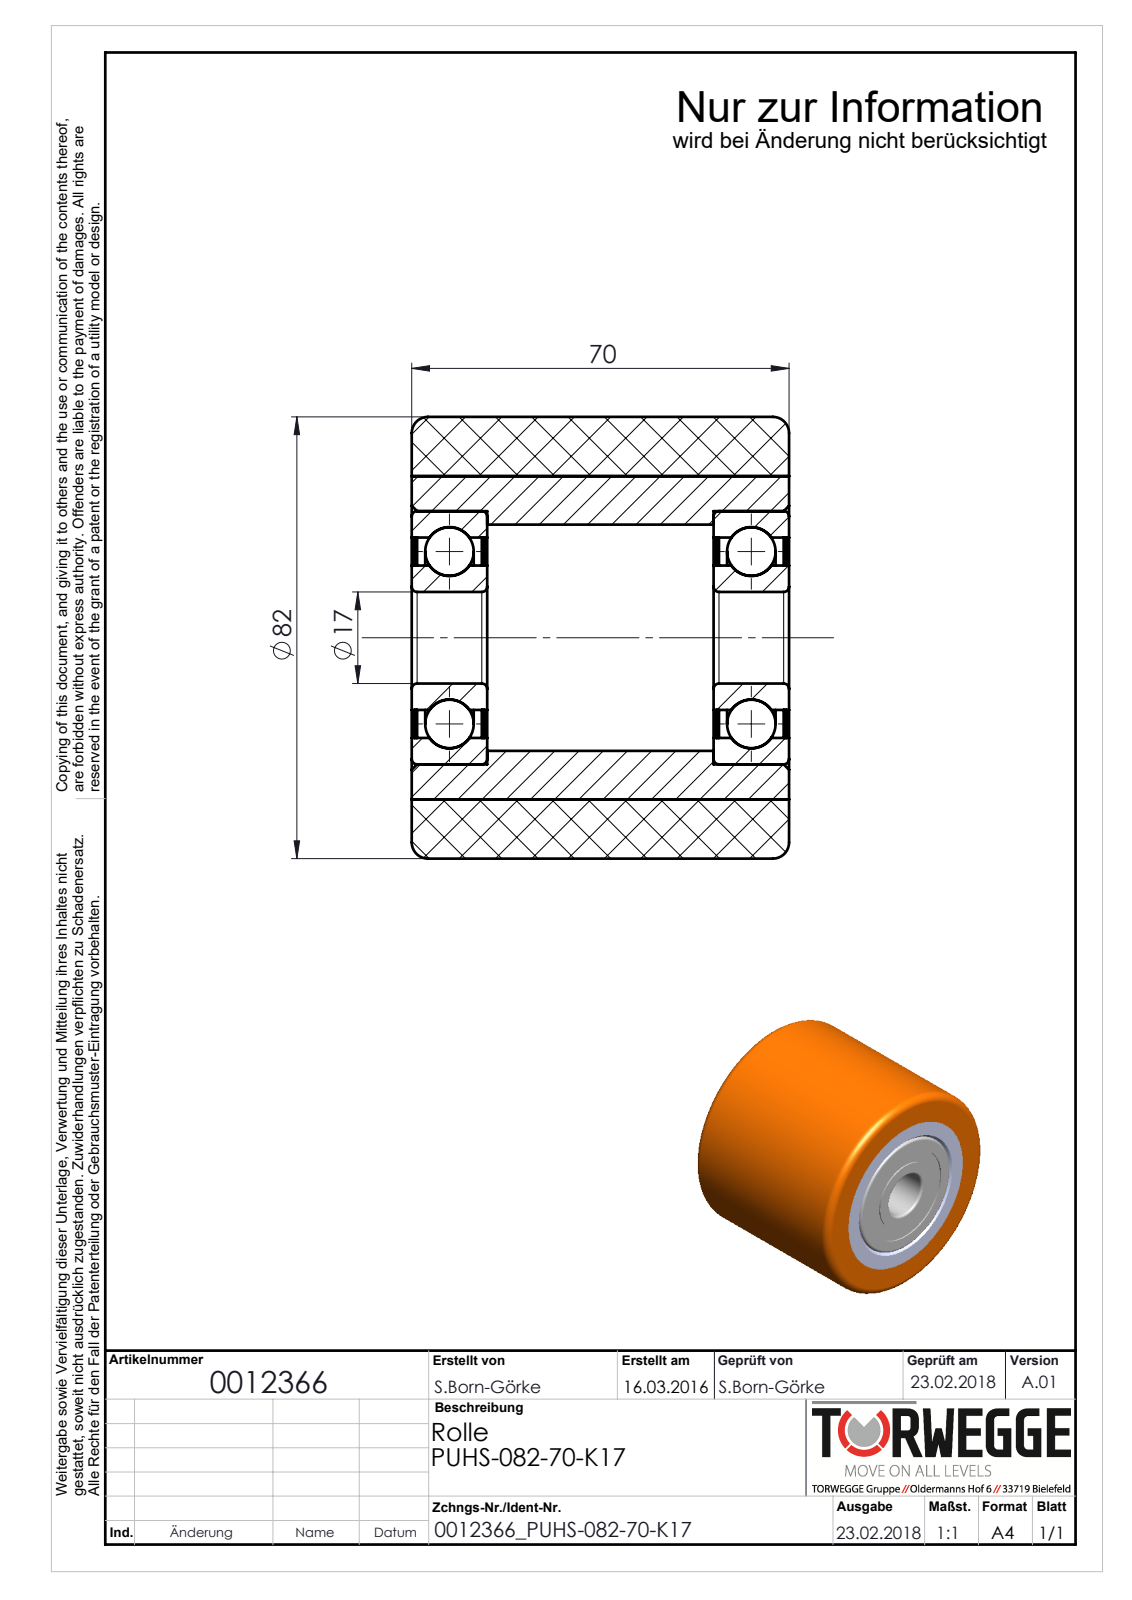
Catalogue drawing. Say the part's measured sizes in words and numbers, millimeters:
The part is named "0012366_PUHS-082-70-K17". Its 3-D file was written by "SolidWorks 2016 (AUTOMOTIVE_DESIGN)". It is 12 solids with 118 faces: 22 planar, 52 cylindrical and 44 other. Overall it measures 82 by 82 by 70 millimeters. Its volume is 298 738 cubic millimeters and its surface area 86 709 square millimeters. Round holes: 1 of diameter 17, 1 of diameter 26.8, 1 of diameter 37.2, 1 of diameter 42, 1 of diameter 47, 1 of diameter 60. Round bosses or shafts: 1 of diameter 82. The main face-to-face distances are 56, 0.5, 70, 13, 14, 1, 13.5, 56.5, 12.5, 55.5.
